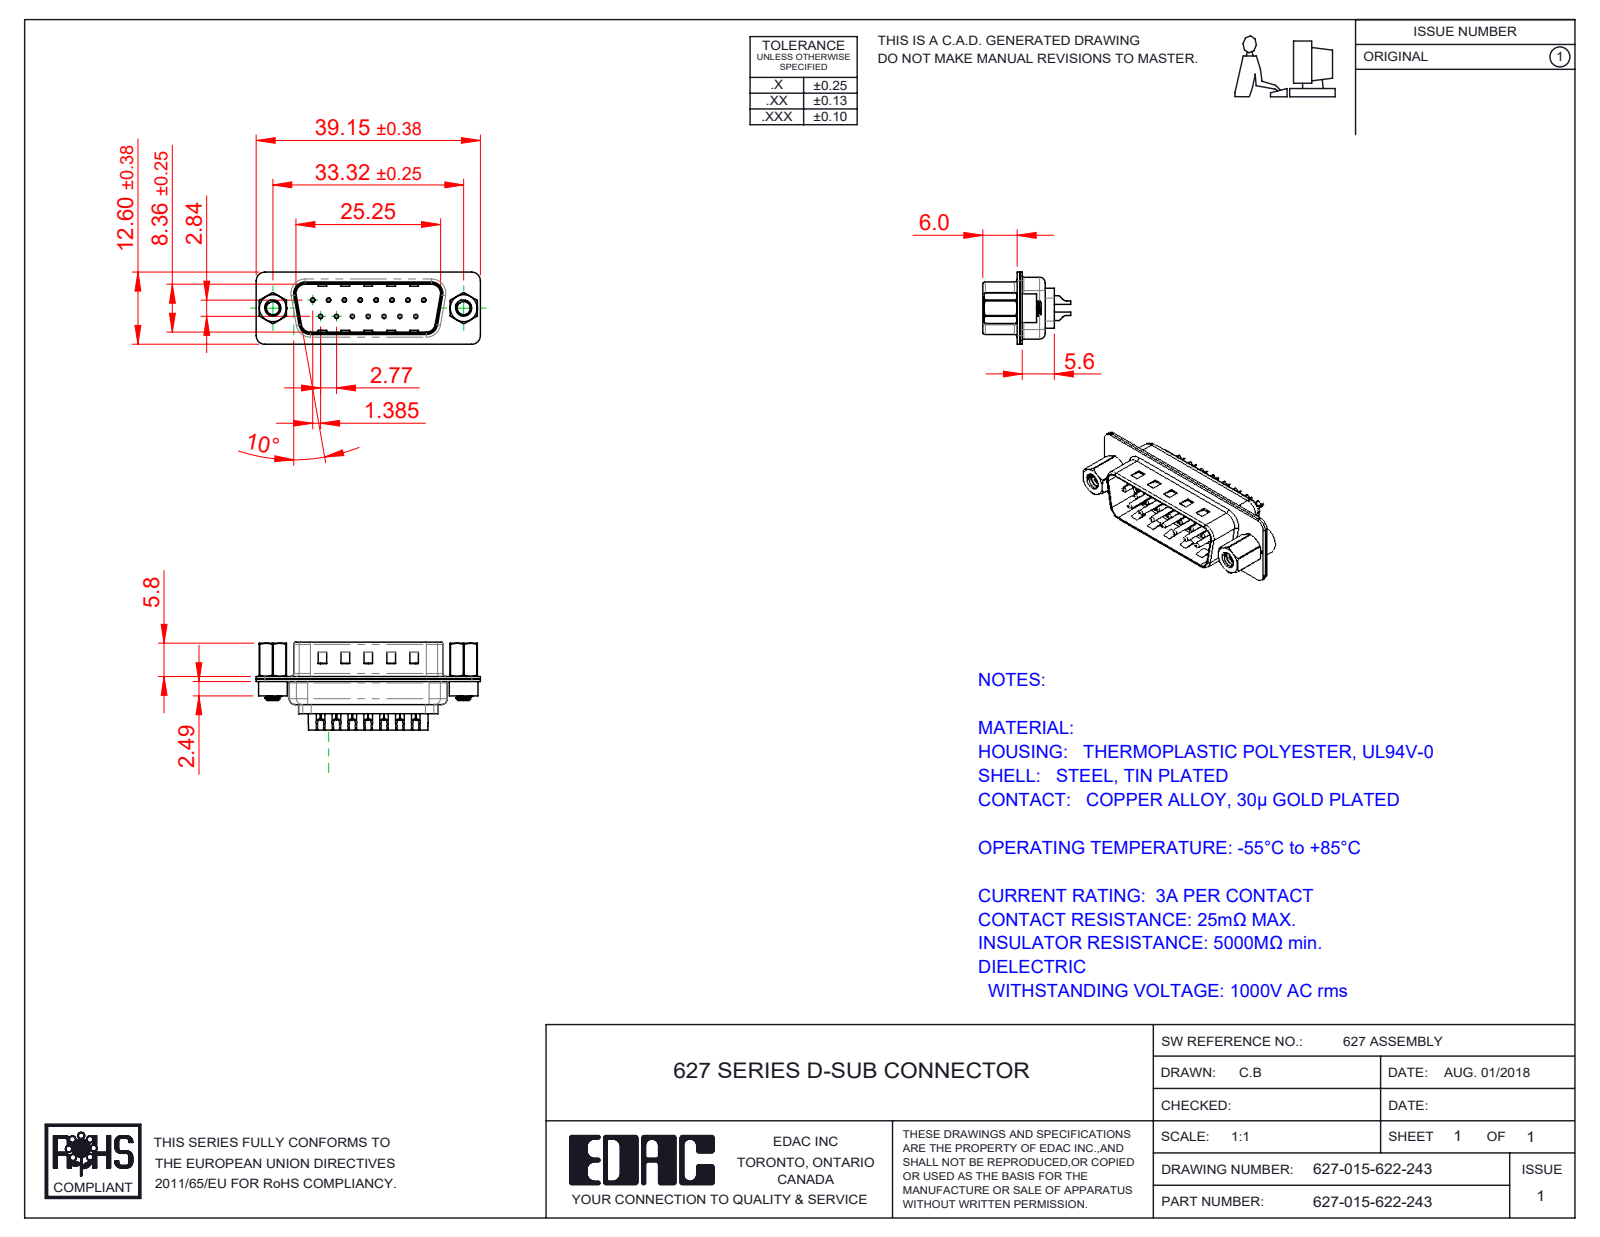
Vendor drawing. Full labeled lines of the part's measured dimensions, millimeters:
Part name (STEP PRODUCT): 627 Shell Front_15 Contacts; 627 Housing_15 LP; 627 Contact Row 2_22L; 627 Shell Rear_15 Contacts (+4 more)
STEP written by: SolidWorks 2020 (CONFIG_CONTROL_DESIGN)
Units: millimetres
Bodies: 22 solids, 1422 faces (371 planar, 638 cylindrical, 413 other)
Overall size (bounding box): 39.15 × 15.35 × 12.6
Volume: 2 043 mm³ · Surface area: 5 895 mm²
Round holes (diameter × count): ⌀0.35 ×15, ⌀1.1 ×15, ⌀1.6 ×15, ⌀2.26 ×2, ⌀2.29 ×2, ⌀4 ×2, ⌀4.8 ×2
Round bosses / shafts (diameter × count): ⌀2 ×15, ⌀1.5 ×15, ⌀0.75 ×15, ⌀5 ×2, ⌀4.9 ×2, ⌀2.79 ×2
Partial cylindrical surfaces — rounded edges, fillets, slot ends (radius × count): R1.5 ×16, R2 ×12, R0.5 ×8, R1.6 ×8, R1 ×6, R0.25 ×4, R0.6 ×4, R0.65 ×4
Main face-to-face distances: 0.4, 0.45, 0.9, 0.82, 9.58, 8.76, 1.5, 1.4, 6.5, 5.6
Hole centre spacings: 3.16, 2.77, 5.54, 8.31, 11.08, 5.03, 5.04, 7.48
